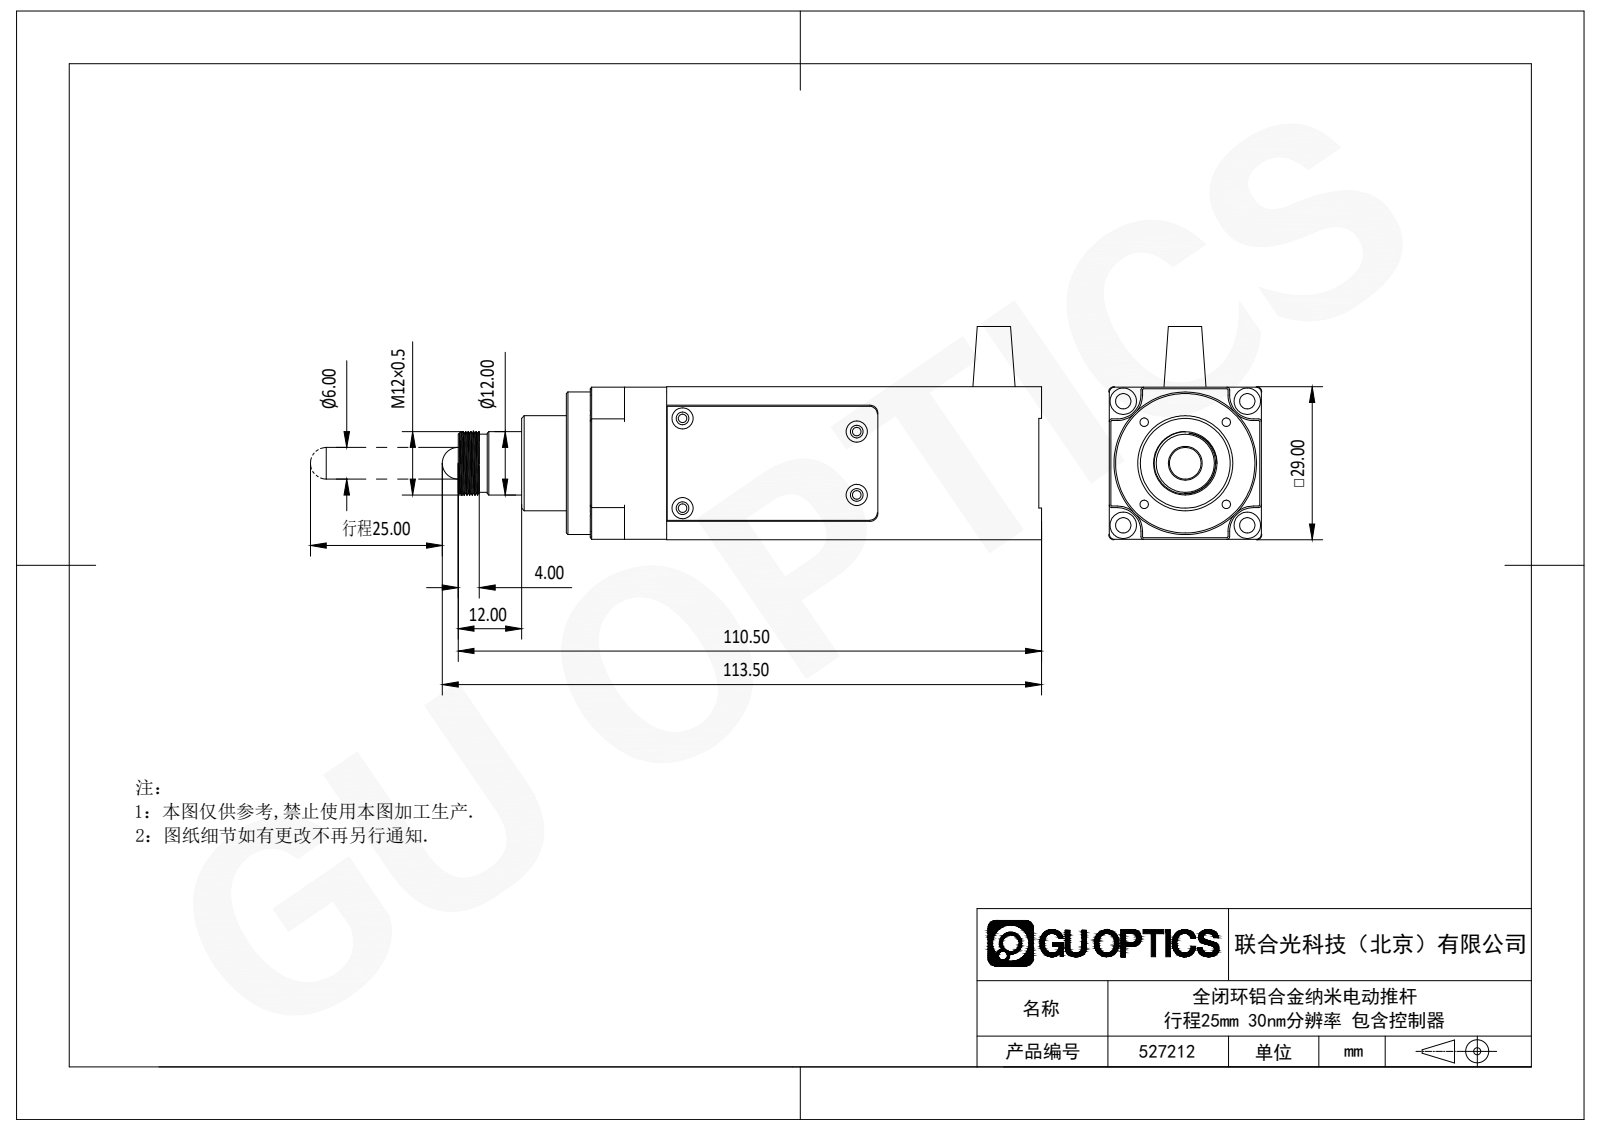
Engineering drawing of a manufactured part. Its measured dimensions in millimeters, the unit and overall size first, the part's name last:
Units: millimetres
Overall size (bounding box): 113.5 × 40.4 × 29
Round holes (diameter × count): ⌀5 ×4, ⌀1 ×1, ⌀11 ×1, ⌀12 ×1, ⌀18 ×1, ⌀27 ×1
Round bosses / shafts (diameter × count): ⌀1.6 ×12, ⌀2.5 ×10, ⌀4 ×8, ⌀2.4 ×8, ⌀5 ×4, ⌀6.4 ×1, ⌀6 ×1
Partial cylindrical surfaces — rounded edges, fillets, slot ends (radius × count): R1.5 ×10, R0.5 ×8, R1 ×8, R2 ×4, R4.5 ×4
Main face-to-face distances: 28.9, 29, 28.8, 27.5, 1.5, 27.4, 1.4, 70.5, 4.5, 6
Hole centre spacings: 25.32, 26.78, 50.06, 52.06, 12, 17
Bodies: 0 solids, 379 faces (136 planar, 183 cylindrical, 60 other)
Part name (STEP PRODUCT): 527212
STEP written by: SolidWorks 2020 (CONFIG_CONTROL_DESIGN)
